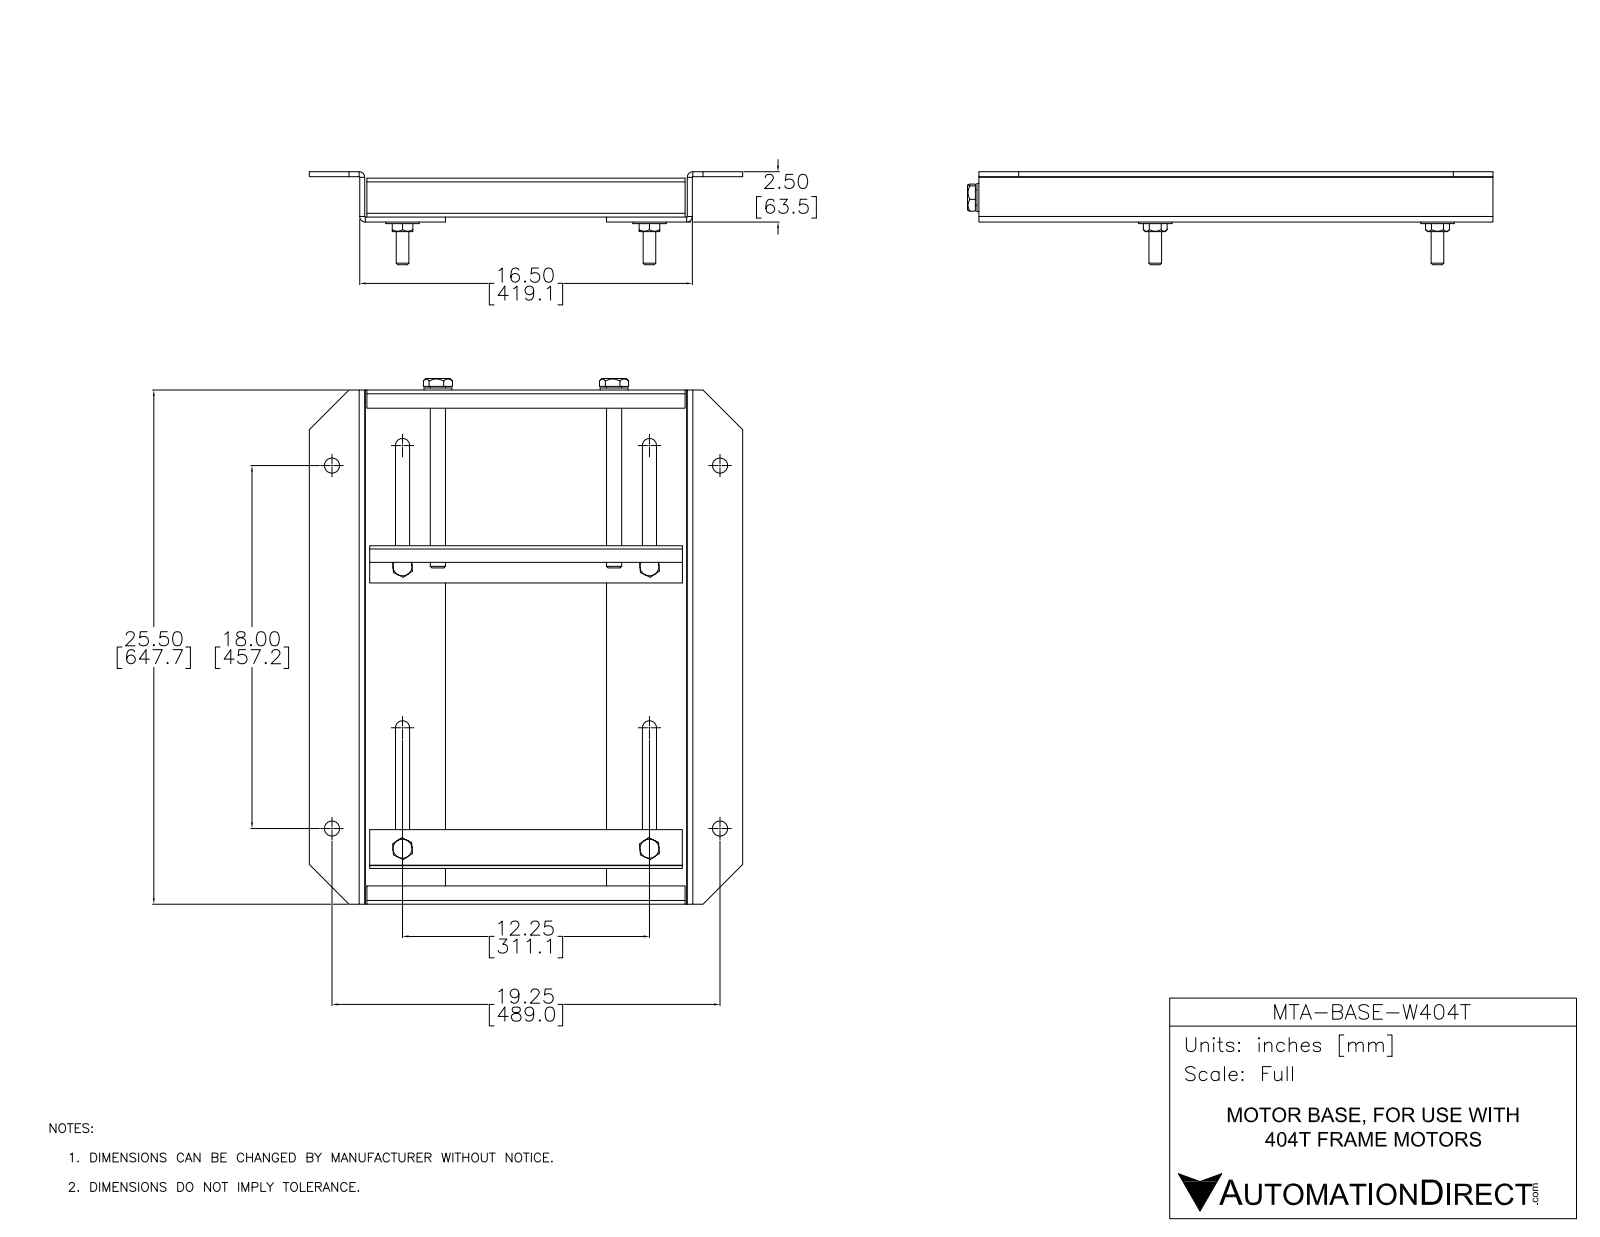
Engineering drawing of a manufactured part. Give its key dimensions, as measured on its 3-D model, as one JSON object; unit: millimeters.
{"part_name": "W404T", "step_written_by": "SolidWorks 2017 (AUTOMOTIVE_DESIGN)", "units": "millimeters", "bodies": {"solids": 34, "faces": 426, "planar": 240, "cylindrical": 110, "other": 76}, "overall_size": [746.4, 568.3, 142.1], "volume_mm3": 3528000, "surface_area_mm2": 1282000, "round_holes": [[19.1, 6], [20, 6], [19.1, 4], [22, 2], [22.2, 2], [22.2, 2]], "round_bosses_or_shafts": [[42, 6]], "partial_cylinders_radius": [[0.7, 11], [10.5, 8], [5.2, 6], [7.1, 4], [4.7, 1]], "face_to_face_distances": [6.4, 69.9, 4.5, 63.5, 76.2, 412.8, 57.5, 419.1, 406.4, 4], "hole_center_spacings": [311.2, 406.4, 501.7, 508, 511.8, 713.9, 102.5, 102.7]}
